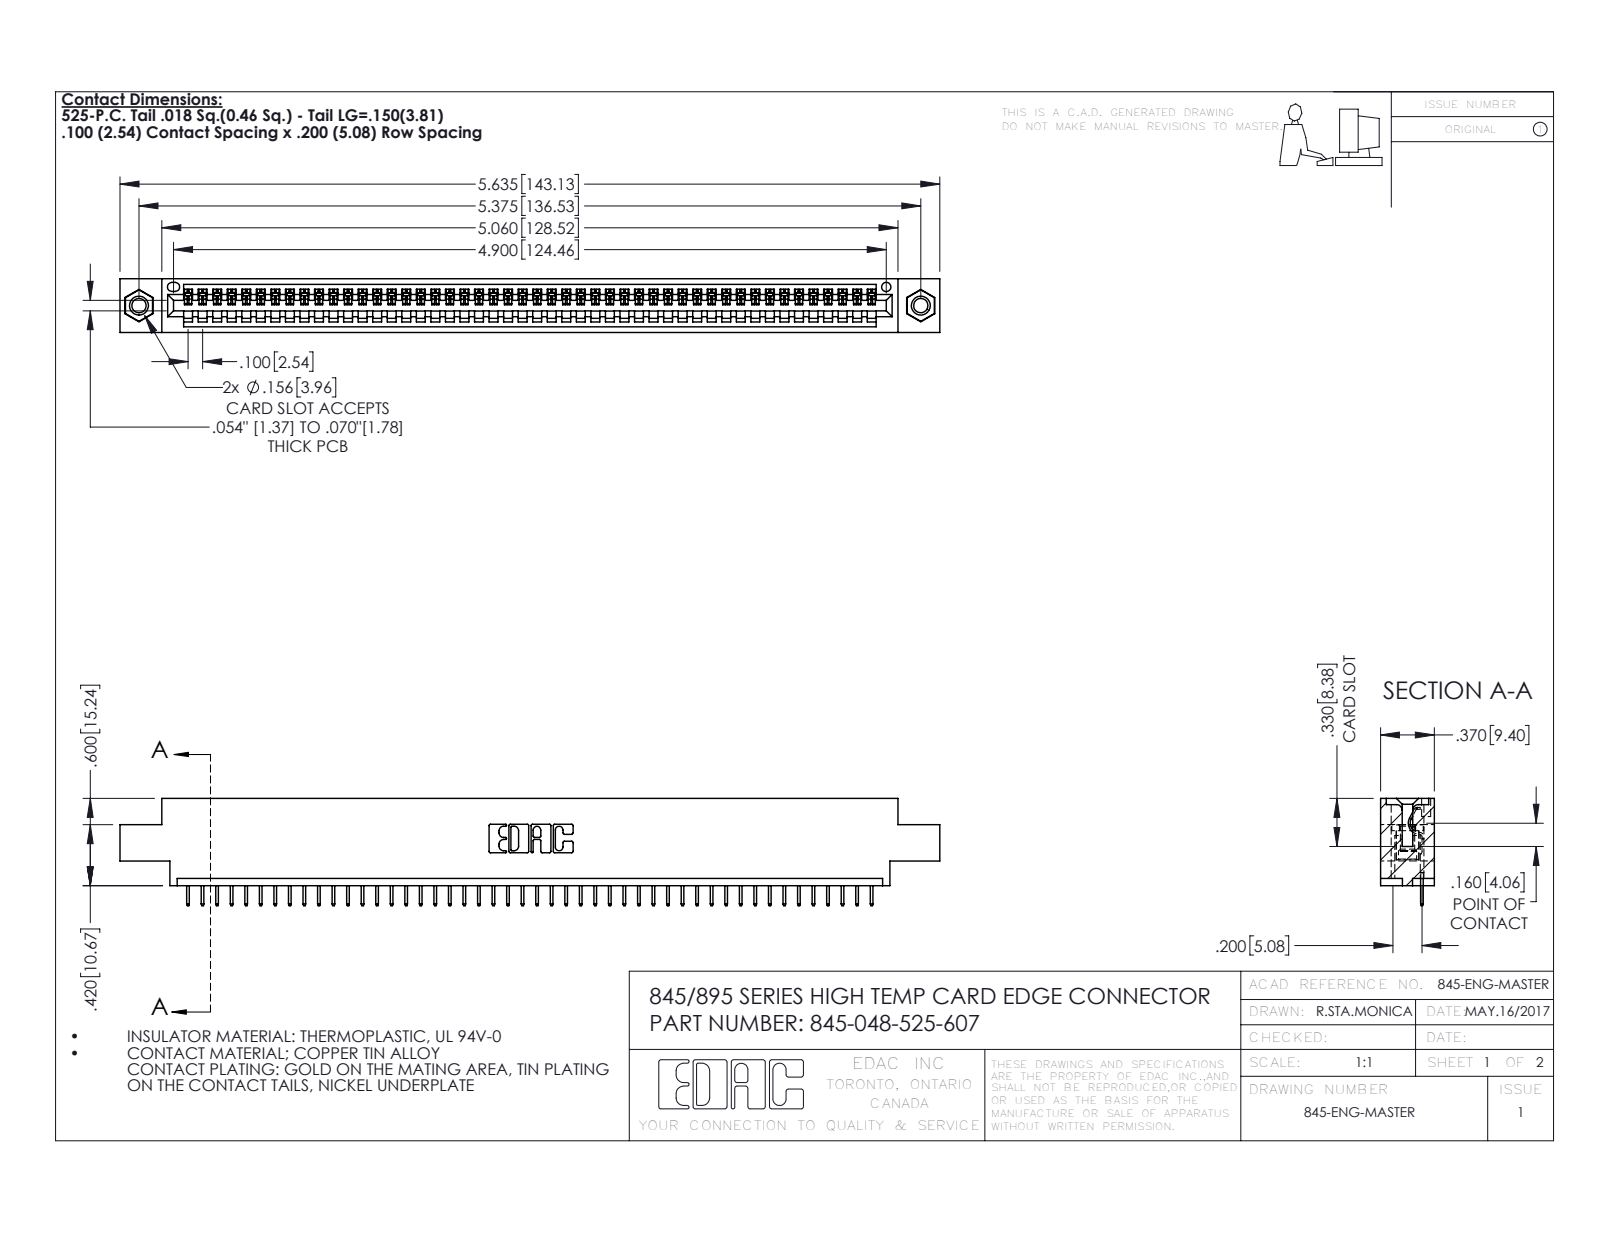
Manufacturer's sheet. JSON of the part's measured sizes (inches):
{"part_name": "845 Part_0.170 Offset - 0.156 Dia-TI; 345-250-001_345-250-005-103; 845-048-525-607; 345-292-001_345-293-125", "step_written_by": "SolidWorks 2020 (CONFIG_CONTROL_DESIGN)", "units": "inches", "bodies": {"solids": 51, "faces": 3166, "planar": 2324, "cylindrical": 826, "other": 16}, "overall_size": [5.635, 0.737, 0.37], "volume_in3": 0.813, "surface_area_in2": 26.8, "round_holes": [[0.098, 2], [0.125, 2], [0.156, 2], [0.064, 1]], "round_bosses_or_shafts": [[0.155, 2]], "partial_cylinders_radius": [[0.006, 96], [0.01, 22], [0.007, 6], [0.031, 6], [0.026, 3], [0.031, 2], [0.04, 2], [0.014, 1]], "face_to_face_distances": [0.072, 0.298, 0.37, 0.2, 0.098, 0.272, 0.025, 0.225, 0.072, 0.175], "hole_center_spacings": [0.27, 5.139, 5.375]}
